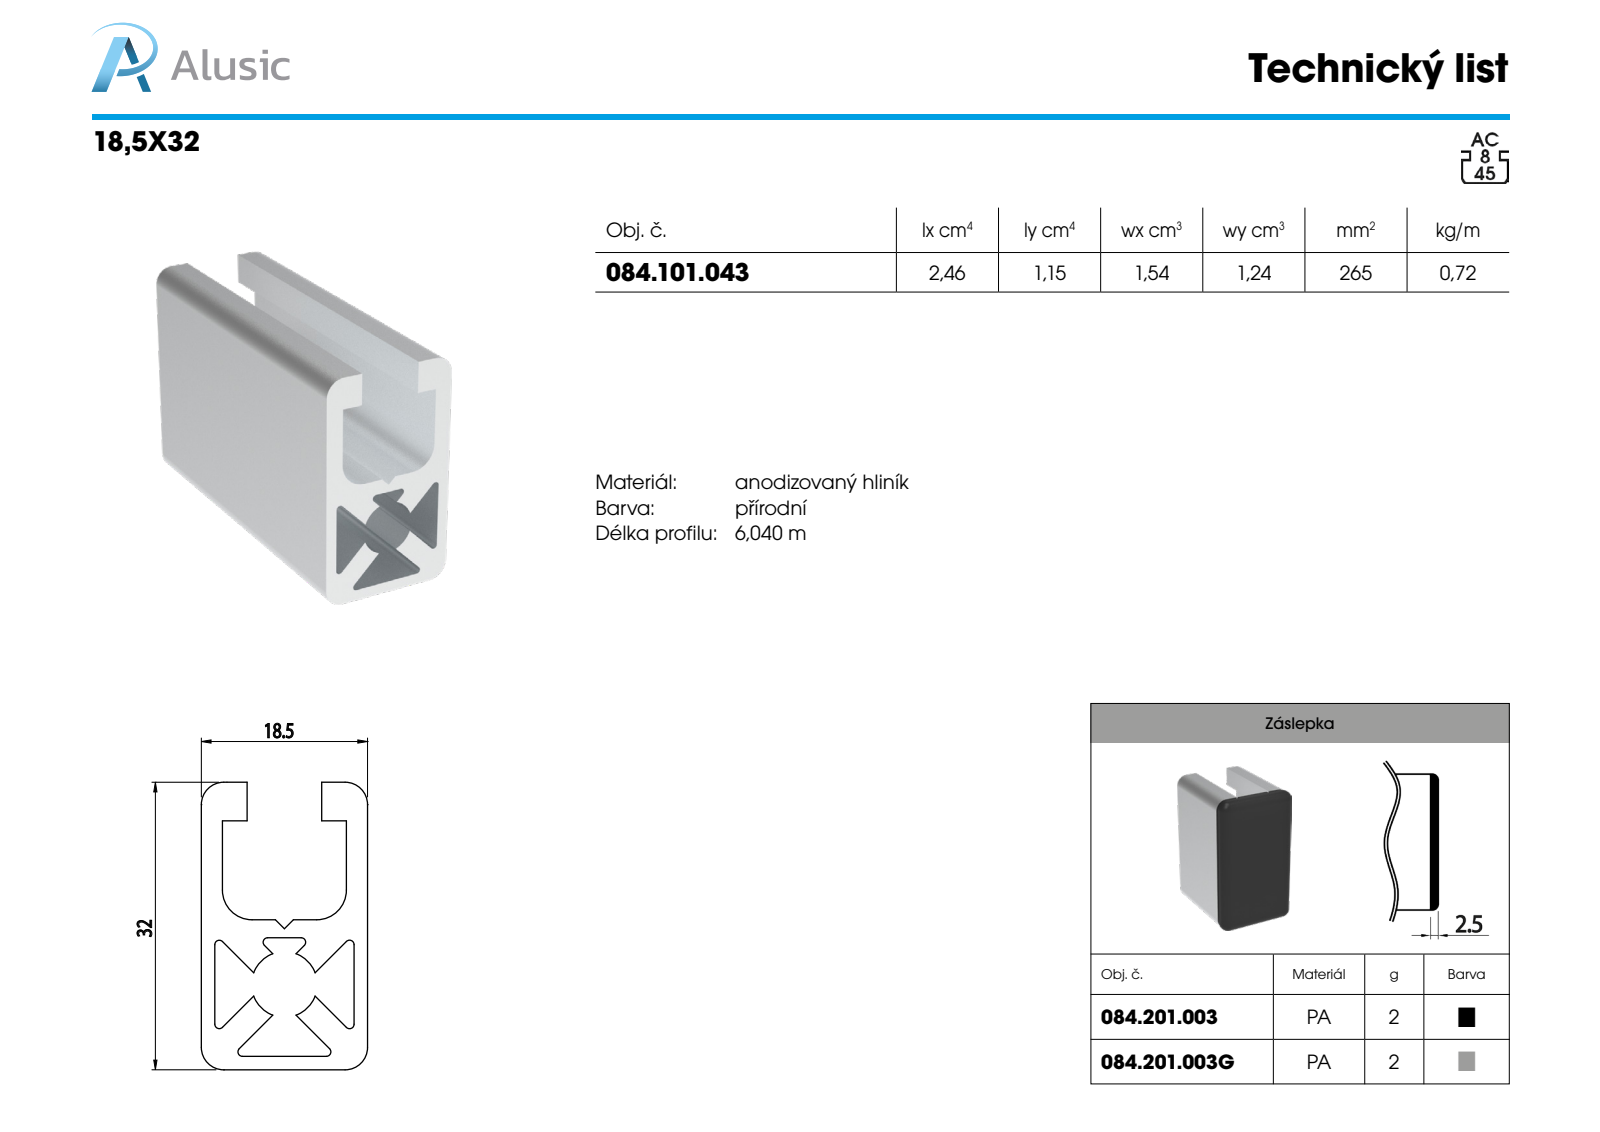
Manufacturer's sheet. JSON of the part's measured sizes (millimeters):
{"part_name": "084.101.043", "step_written_by": "SolidWorks 2018 (AUTOMOTIVE_DESIGN)", "units": "millimeters", "bodies": {"solids": 1, "faces": 49, "planar": 29, "cylindrical": 20, "other": 0}, "overall_size": [100, 32, 18.5], "volume_mm3": 26431, "surface_area_mm2": 22702, "partial_cylinders_radius": [[0.5, 8], [2.5, 4], [3.3, 2], [3.65, 1]], "face_to_face_distances": [1.5, 18.5, 17, 2.35, 16.15, 0.85, 14.65, 3, 15.5, 5.1]}
